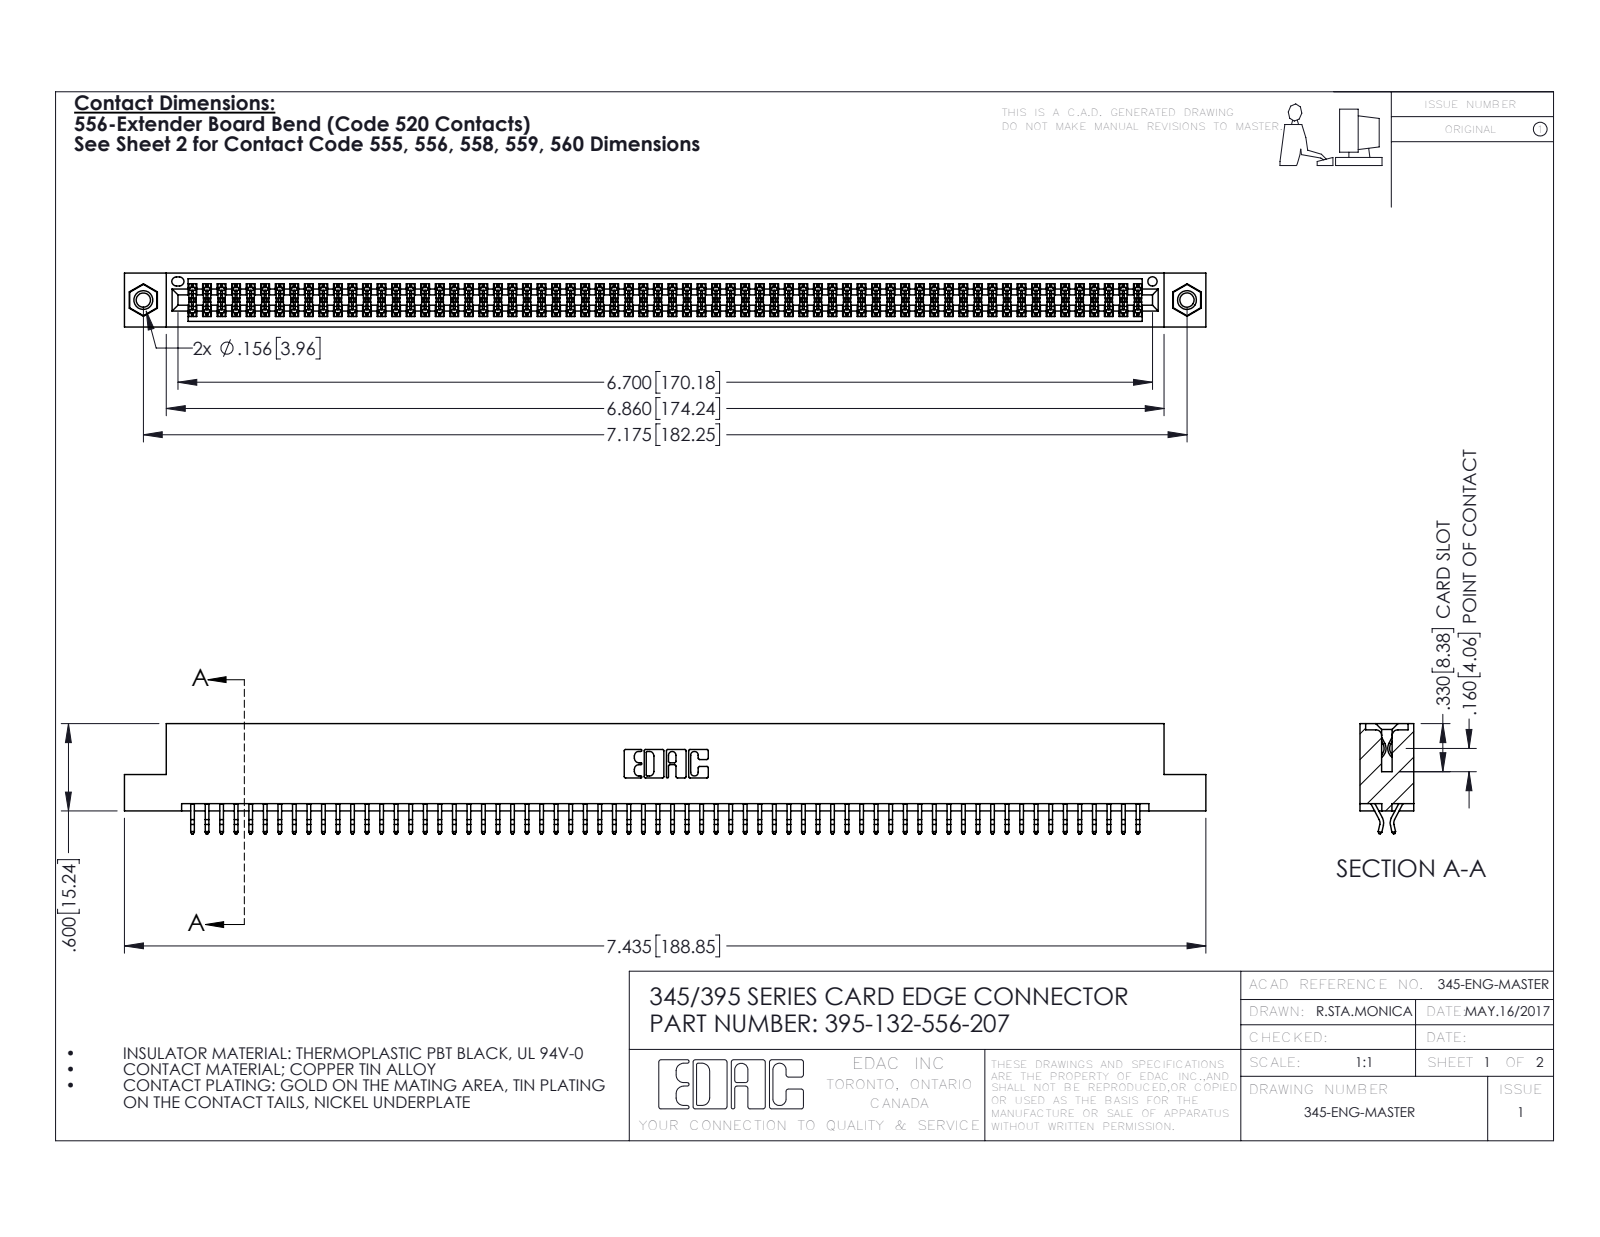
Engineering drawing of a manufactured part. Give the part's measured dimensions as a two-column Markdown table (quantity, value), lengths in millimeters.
| quantity | value |
| --- | --- |
| part name | 345-292-001_556 Tail; 345-250-001_345-250-005-103; 345 Part_Flush Mounting Lugs - 0.156 Dia-TI; 395-132-556-207 |
| STEP written by | SolidWorks 2016 (CONFIG_CONTROL_DESIGN) |
| units | millimeters |
| bodies | 135 solids, 7578 faces (4996 planar, 2566 cylindrical, 16 other) |
| overall size | 188.8 × 19.2 × 9.4 |
| volume | 18 550 mm³ |
| surface area | 27 790 mm² |
| round holes (diameter × count) | 2.5 × 2, 3.2 × 2, 4 × 2, 1.6 × 1 |
| round bosses / shafts (diameter × count) | 3.9 × 2 |
| partial cylindrical surfaces (radius × count) | 0.2 × 198, 0.3 × 22, 0.2 × 6, 0.8 × 6, 0.7 × 3, 0.3 × 2, 0.4 × 2, 0.5 × 2 |
| main face-to-face distances | 1.8, 7.6, 9.4, 5.1, 0.6, 2.5, 6.9, 5.7, 4.4, 3.8 |
| hole center spacings | 6.9, 176.3, 182.2 |
